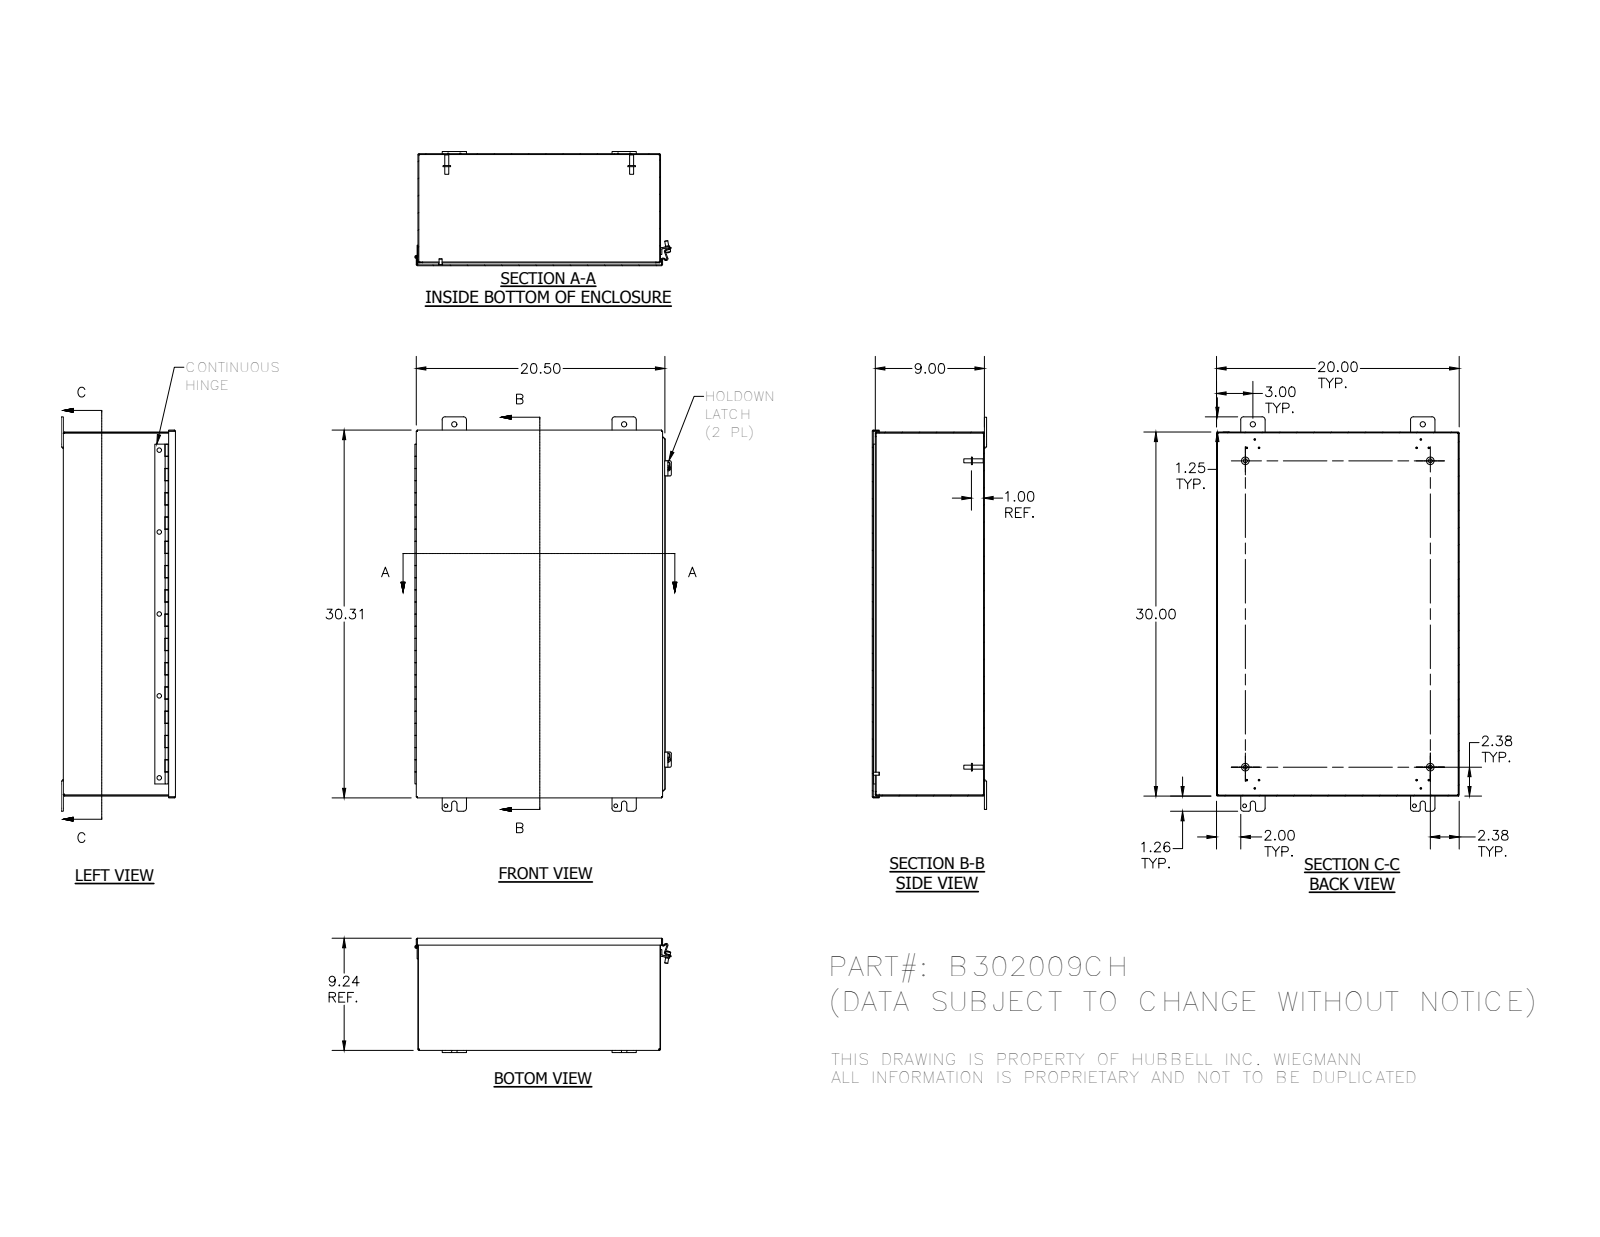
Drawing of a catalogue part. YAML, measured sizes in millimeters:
part_name: "B302009CH; B302009CHBKP; B3020CHLID; H6010102 (+8 more)"
step_written_by: "Autodesk Inventor 2012 (AUTOMOTIVE_DESIGN)"
units: millimeters
bodies: {solids: 20, faces: 698, planar: 431, cylindrical: 198, other: 69}
overall_size: [825.6, 536.9, 239.3]
volume: 2779000
surface_area: 2956000
round_holes:
  - {diameter: 9.5, count: 5}
  - {diameter: 2.8, count: 4}
  - {diameter: 8, count: 4}
  - {diameter: 11.1, count: 4}
  - {diameter: 5, count: 2}
  - {diameter: 3.2, count: 1}
  - {diameter: 3.2, count: 1}
round_bosses_or_shafts:
  - {diameter: 15.9, count: 4}
  - {diameter: 8.4, count: 4}
  - {diameter: 6.4, count: 4}
  - {diameter: 10.4, count: 2}
  - {diameter: 8.7, count: 2}
  - {diameter: 8.6, count: 1}
  - {diameter: 3, count: 1}
partial_cylinders:
  - {radius: 3.2, count: 16}
  - {radius: 6.4, count: 16}
  - {radius: 0.8, count: 8}
  - {radius: 1.6, count: 8}
  - {radius: 1.8, count: 8}
  - {radius: 2.7, count: 8}
  - {radius: 0.4, count: 5}
  - {radius: 2.3, count: 5}
face_to_face_distances: [1.9, 232.9, 234.8, 231, 506.1, 760.1, 508, 504.2, 762, 758.2]
hole_center_spacings: [40.5, 171.5, 355.6, 762.1, 841, 342.9, 19.1, 28.8]
